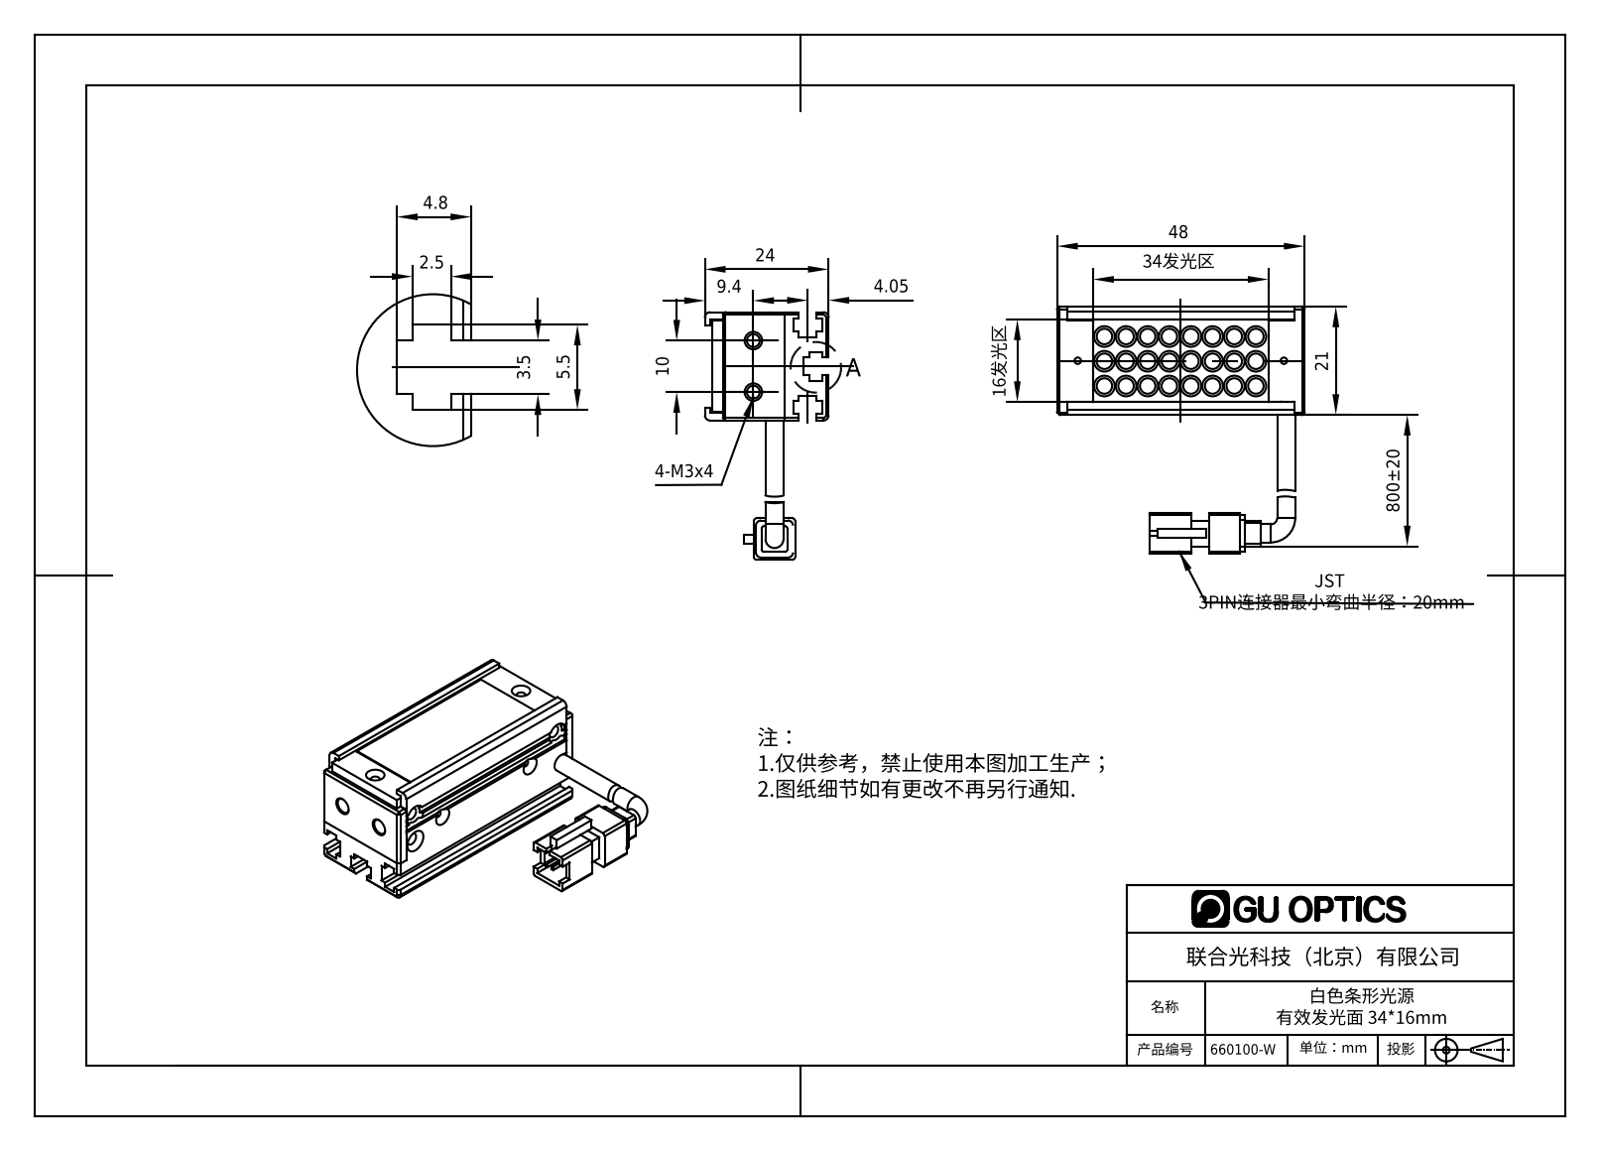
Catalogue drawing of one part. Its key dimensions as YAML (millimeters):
part_name: "660100-W"
step_written_by: "SolidWorks 2016 (AUTOMOTIVE_DESIGN)"
units: millimeters
bodies: {solids: 6, faces: 878, planar: 536, cylindrical: 193, other: 149}
overall_size: [48, 48, 24]
volume: 15504
surface_area: 16054
round_holes:
  - {diameter: 1.25, count: 4}
  - {diameter: 1.6, count: 4}
  - {diameter: 2.4, count: 4}
  - {diameter: 1.7, count: 2}
  - {diameter: 2.5, count: 2}
  - {diameter: 3, count: 2}
  - {diameter: 2, count: 1}
round_bosses_or_shafts:
  - {diameter: 4, count: 24}
  - {diameter: 3, count: 24}
  - {diameter: 3.5, count: 2}
partial_cylinders:
  - {radius: 1, count: 12}
  - {radius: 0.5, count: 8}
  - {radius: 0.99, count: 4}
  - {radius: 1.65, count: 1}
face_to_face_distances: [1, 2.5, 2, 18.5, 20.5, 1.3, 3.5, 12, 8.5, 15.7]
hole_center_spacings: [6, 7.79, 8.45, 31.57, 31.74, 39, 39.46, 10]
